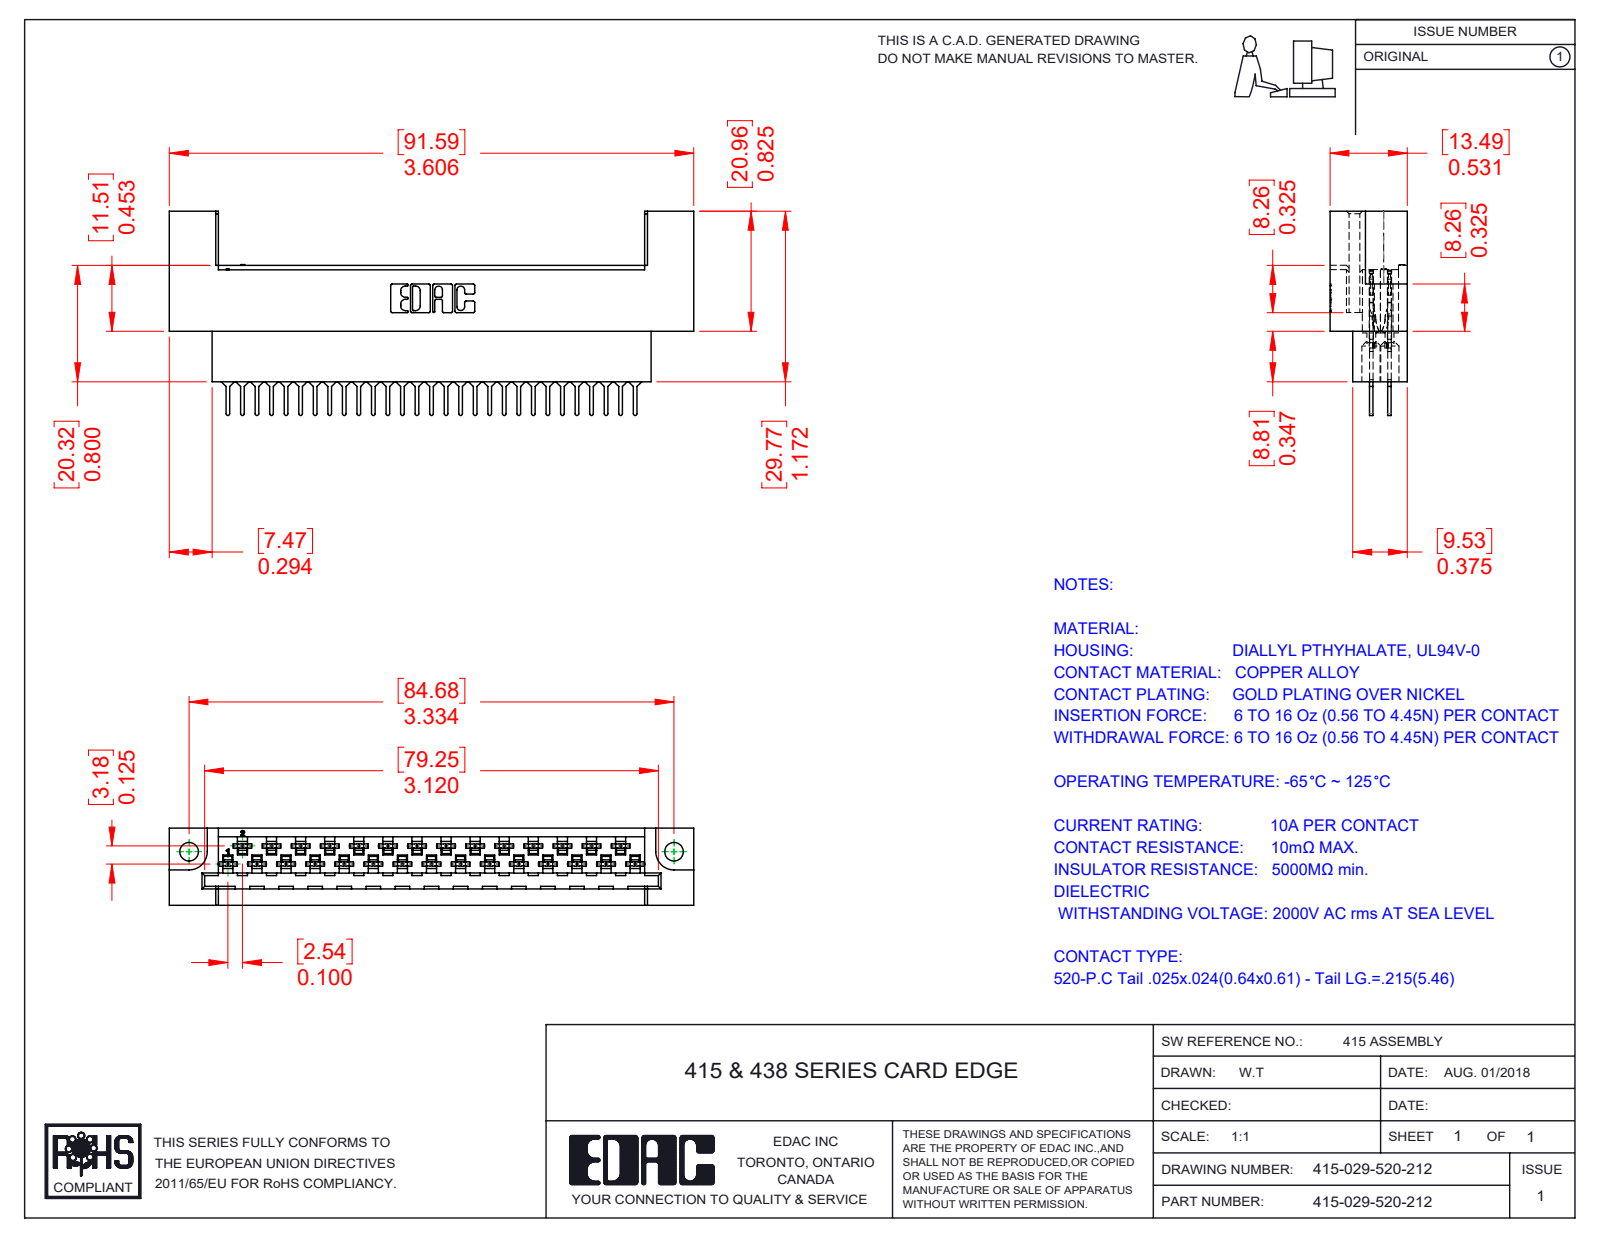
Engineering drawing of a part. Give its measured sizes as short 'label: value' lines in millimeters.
name: 415-029-520-212; 415-210-001_415-210-029-212; 516-290-001_520
written by: SolidWorks 2016 (CONFIG_CONTROL_DESIGN)
unit: mm
bodies: 30 solids, 3002 faces (1919 planar, 800 cylindrical, 283 other)
size: 91.59 × 35.65 × 13.49
volume: 16 332 mm³; area: 19 527 mm²
holes: 29× ⌀1.27, 29× ⌀3.3, 2× ⌀3.25
rounds: 116× R0.3, 116× R0.56, 58× R0.18, 58× R0.2, 58× R0.41, 58× R2.03, 29× R0.32, 22× R0.25
face distances: 3.18, 0.61, 1.88, 13.49, 1.27, 7.49, 6.61, 6.88, 6, 9.53
hole spacings: 5.08, 10.16, 15.24, 20.32, 25.4, 30.48, 35.56, 2.54
